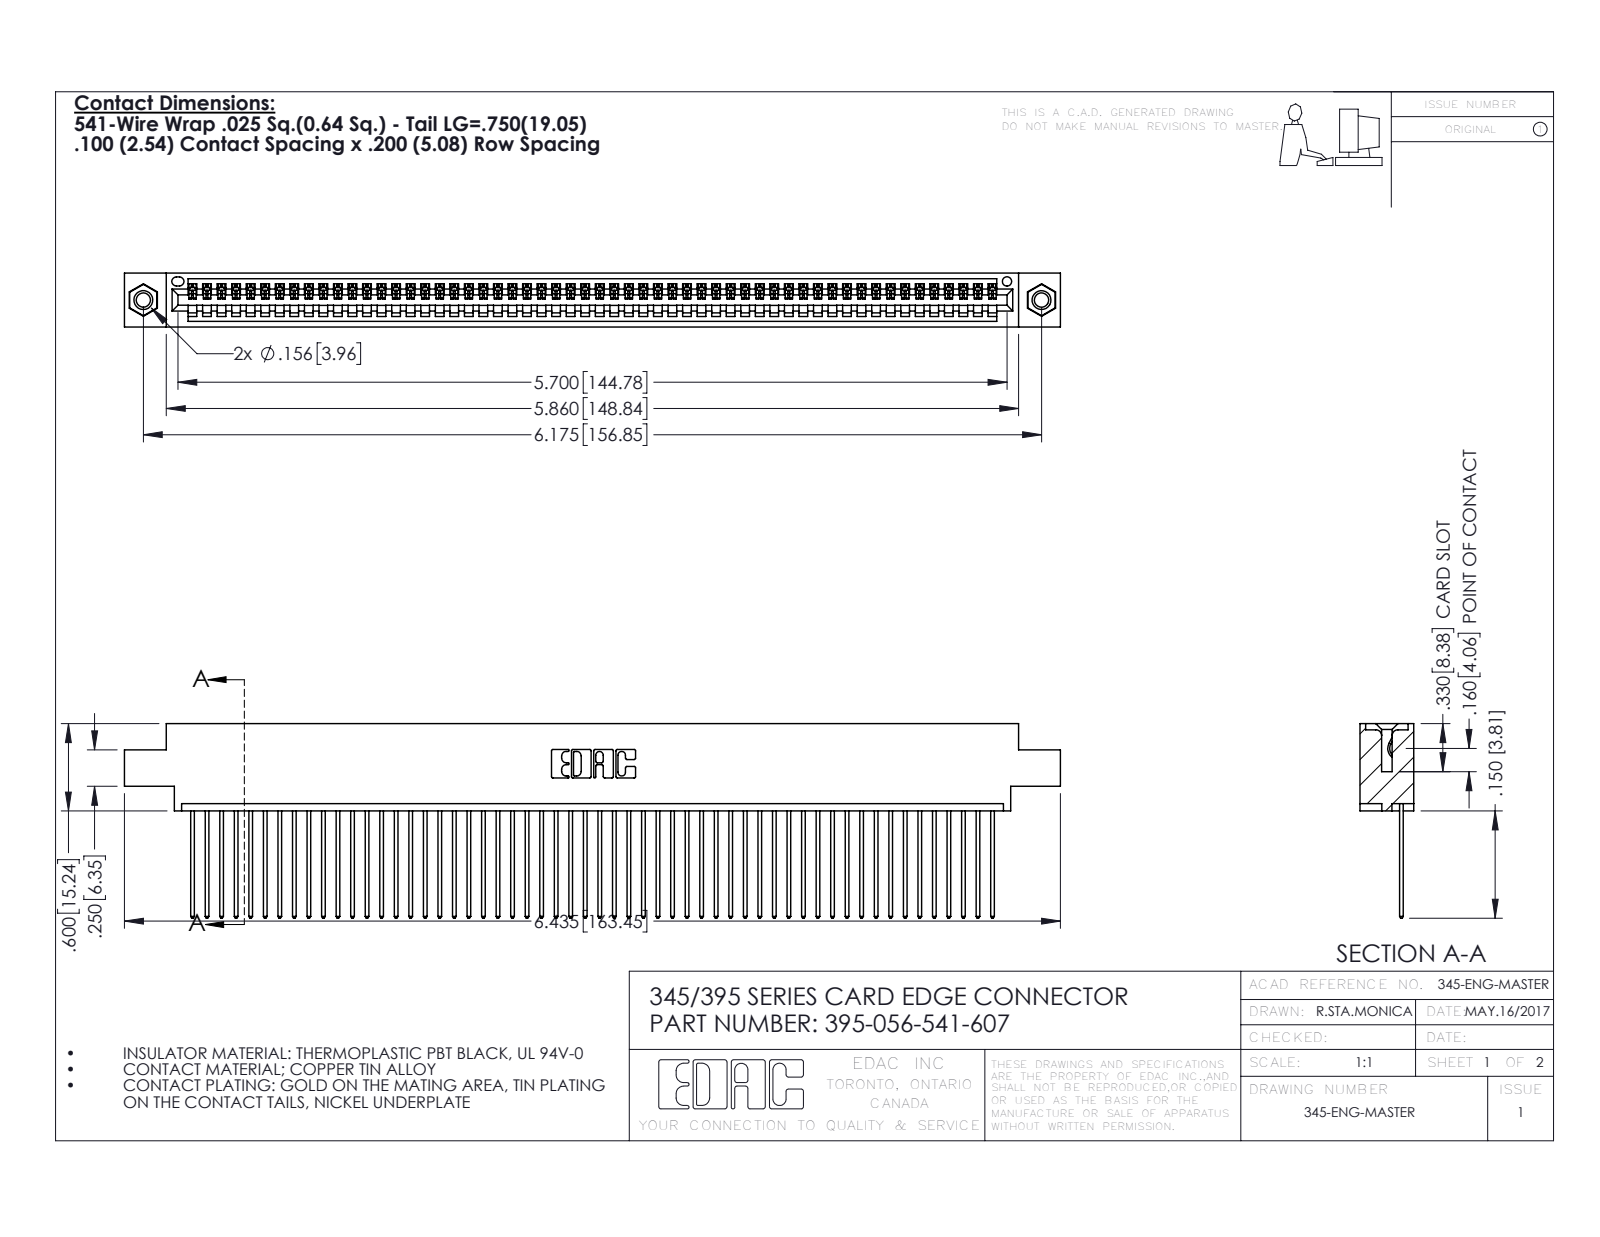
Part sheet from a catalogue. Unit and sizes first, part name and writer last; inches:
Units: inches
Overall size (bounding box): 6.435 × 1.337 × 0.37
Round holes (diameter × count): ⌀0.098 ×2, ⌀0.125 ×2, ⌀0.156 ×2, ⌀0.064 ×1
Round bosses / shafts (diameter × count): ⌀0.155 ×2
Partial cylindrical surfaces — rounded edges, fillets, slot ends (radius × count): R0.006 ×112, R0.01 ×112, R0.01 ×22, R0.007 ×6, R0.031 ×6, R0.026 ×3, R0.031 ×2, R0.04 ×2
Main face-to-face distances: 0.072, 0.298, 0.098, 0.272, 0.025, 0.37, 0.2, 0.225, 0.175, 0.149
Hole centre spacings: 0.27, 5.939, 6.175
Volume: 0.958 in³ · Surface area: 34.56 in²
Bodies: 59 solids, 3438 faces (2356 planar, 1066 cylindrical, 16 other)
Part name (STEP PRODUCT): 395-056-541-607; 345-292-001_345-293-141; 345-250-001_345-250-005-103; 345 Part_0.170 Offset - 0.156 Dia-TI
STEP written by: SolidWorks 2016 (CONFIG_CONTROL_DESIGN)
